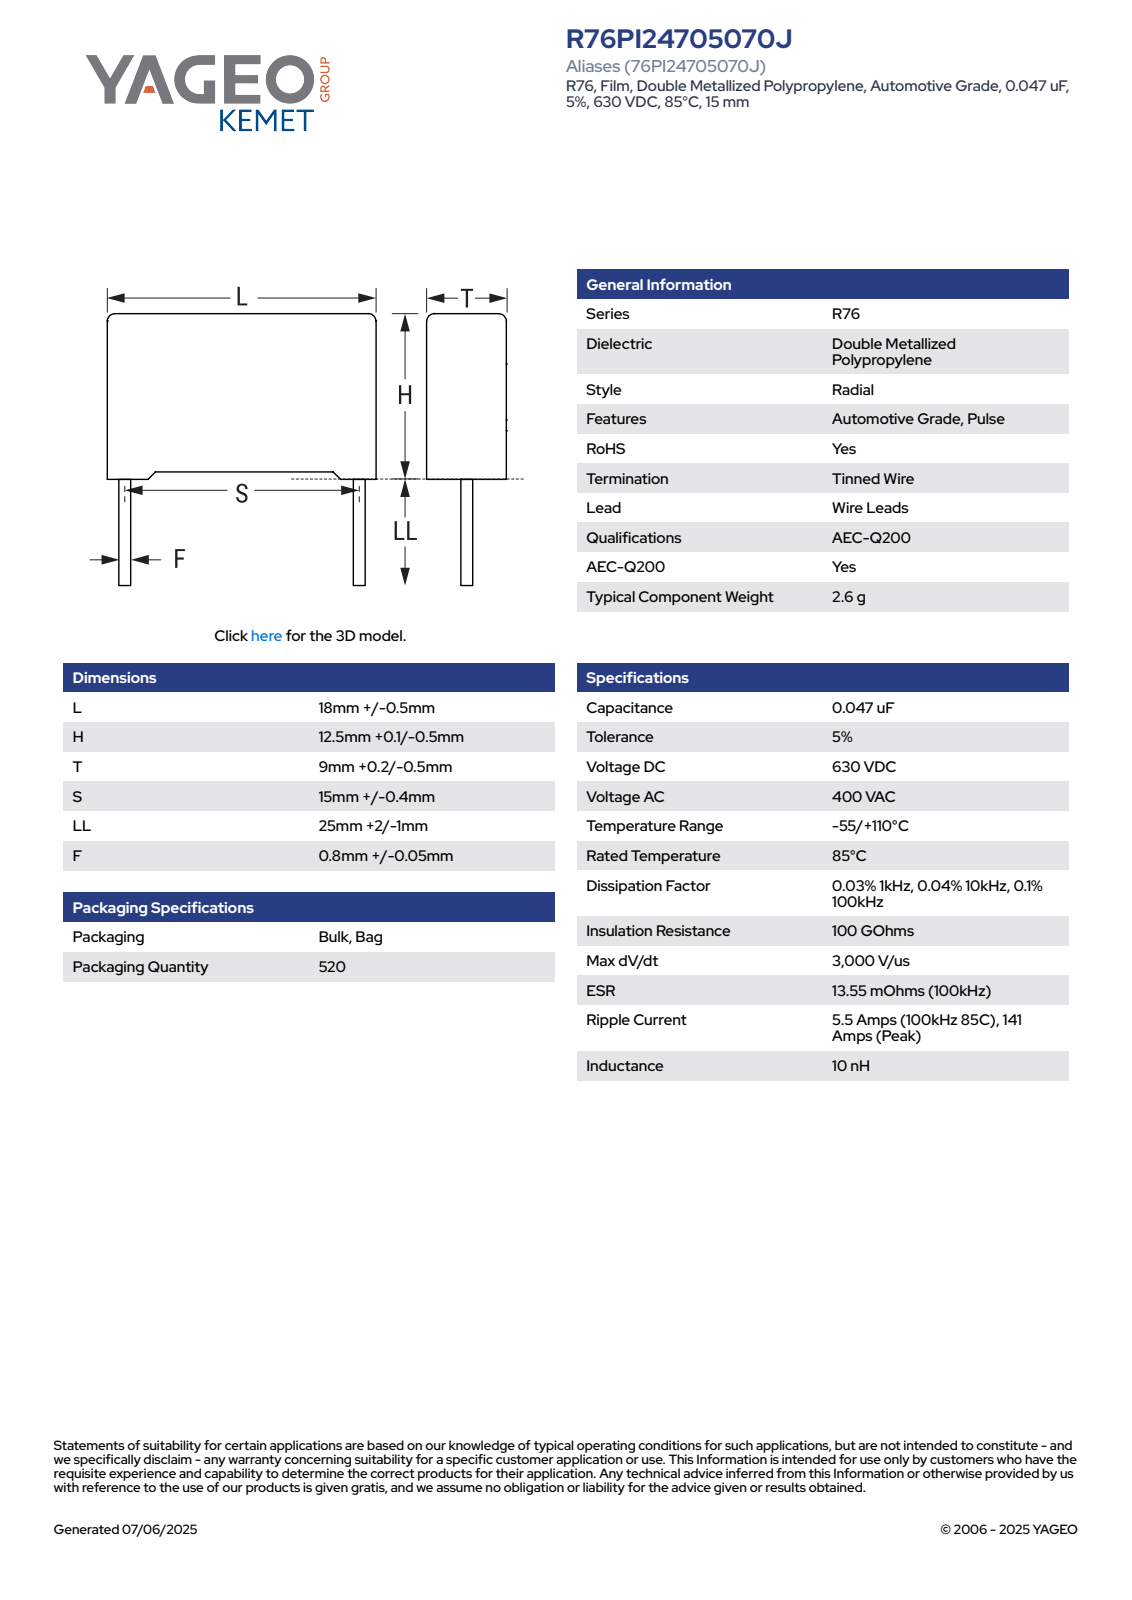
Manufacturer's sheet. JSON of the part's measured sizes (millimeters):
{"part_name": "CFR_RB2_18X12.5X9_L18.5H12.6T9.2S15LL27F0.85", "step_written_by": "SolidWorks 2021 (AUTOMOTIVE_DESIGN)", "units": "millimeters", "bodies": {"solids": 4, "faces": 85, "planar": 77, "cylindrical": 8, "other": 0}, "overall_size": [39.6, 18.5, 9.21], "volume_mm3": 2064, "surface_area_mm2": 1219, "round_bosses_or_shafts": [[0.85, 2]], "partial_cylinders_radius": [[0.5, 4]], "face_to_face_distances": [9.2, 11.85, 18.5, 0.62, 0.75, 12.6, 8.58, 0.43, 0.32, 12.17]}
